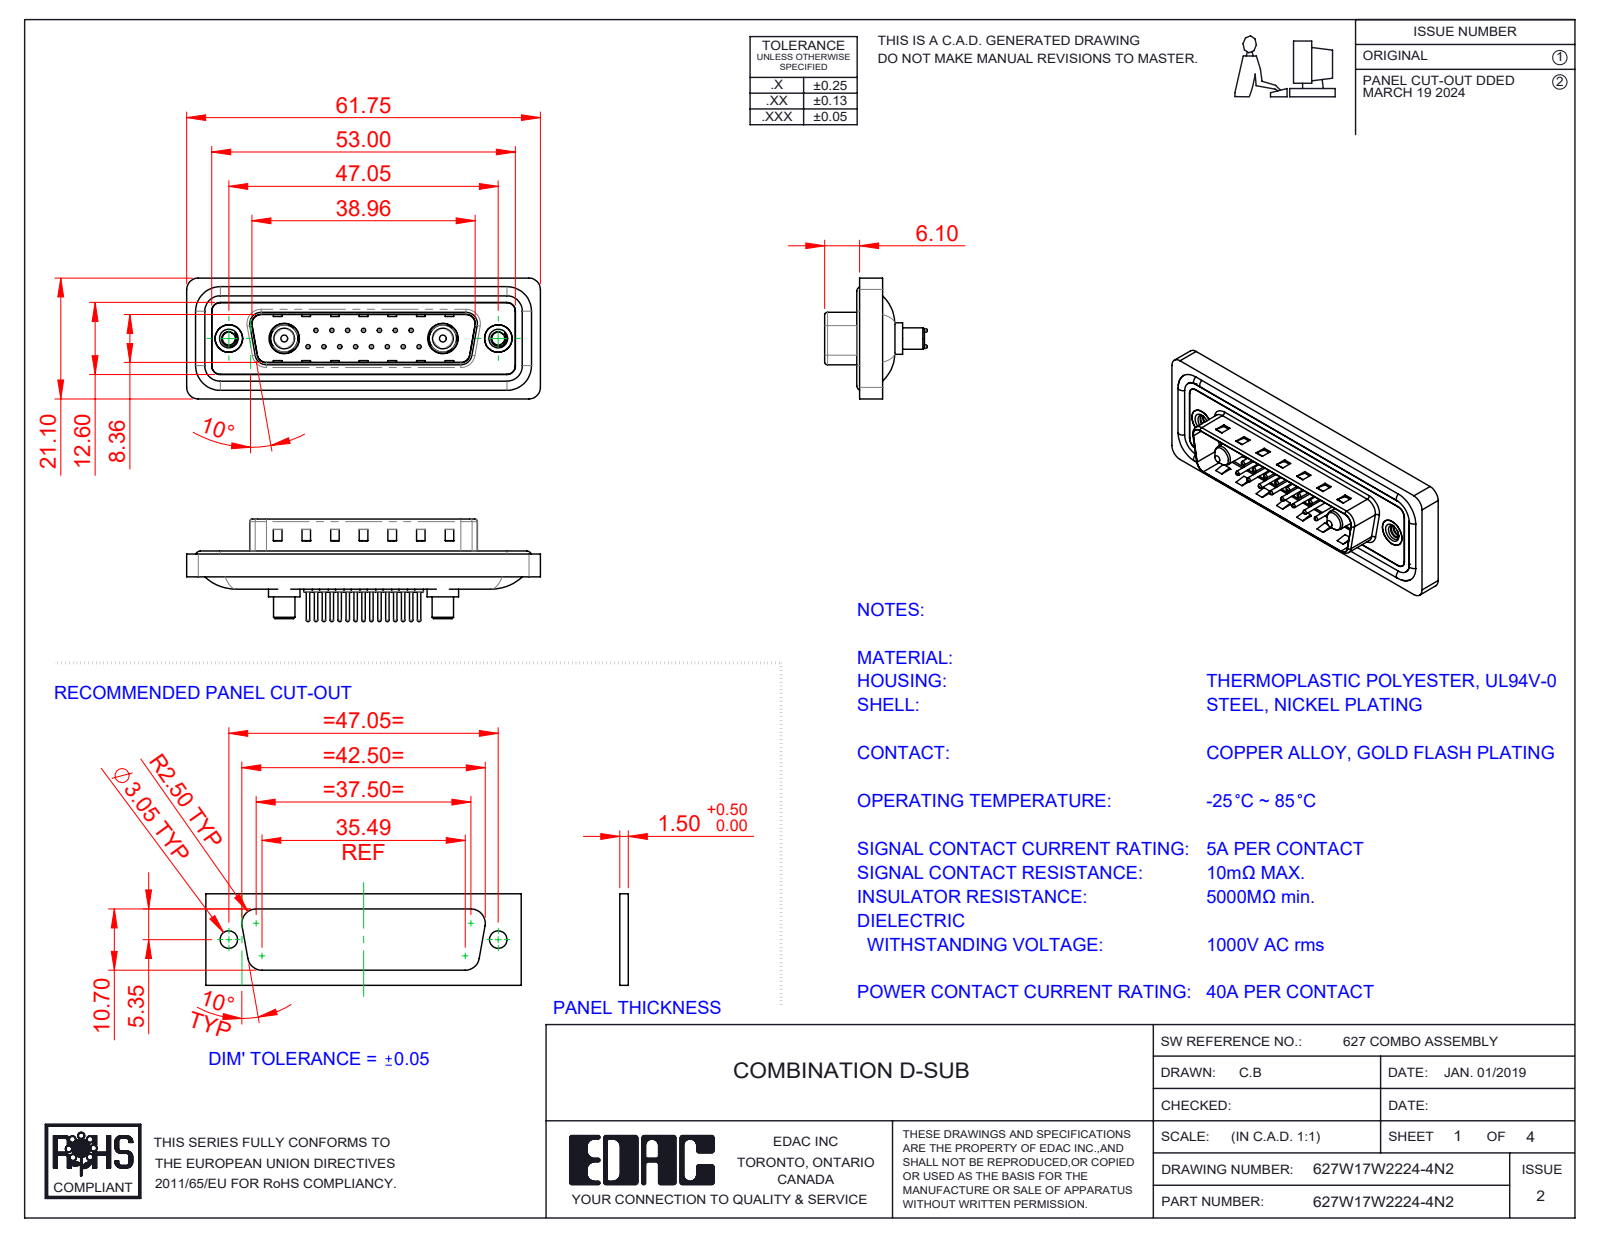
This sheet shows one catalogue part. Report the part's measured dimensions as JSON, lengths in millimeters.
{"part_name": "627Combo Shell Front_25 Contacts; 627Combo Contact Row 2_24; 627Combo Contact Row 1_24; 627Combo Threaded Rivet_2 (+5 more)", "step_written_by": "SolidWorks 2023 (CONFIG_CONTROL_DESIGN)", "units": "millimeters", "bodies": {"solids": 26, "faces": 1116, "planar": 334, "cylindrical": 436, "other": 346}, "overall_size": [61.75, 21.1, 17.9], "volume_mm3": 7303, "surface_area_mm2": 11936, "round_holes": [[0.75, 15], [1.6, 15], [2, 15], [2.26, 2], [4, 2], [4.8, 2], [4.85, 2], [5, 2], [5.3, 2]], "round_bosses_or_shafts": [[1.5, 15], [0.6, 15], [1.6, 4], [5.5, 2], [5.2, 2], [4.9, 2], [4.75, 2], [3.75, 2]], "partial_cylinders_radius": [[1.5, 22], [2, 18], [0.5, 8], [1.6, 8], [0.25, 4], [0.6, 4], [0.65, 4], [0.9, 4]], "face_to_face_distances": [0.4, 1.5, 1.1, 1.6, 0.5, 3.1, 2.9, 0.82, 9.58, 4.1], "hole_center_spacings": [3.16, 2.77, 5.54, 8.31, 5.04, 7.49, 11.08, 5.03]}
